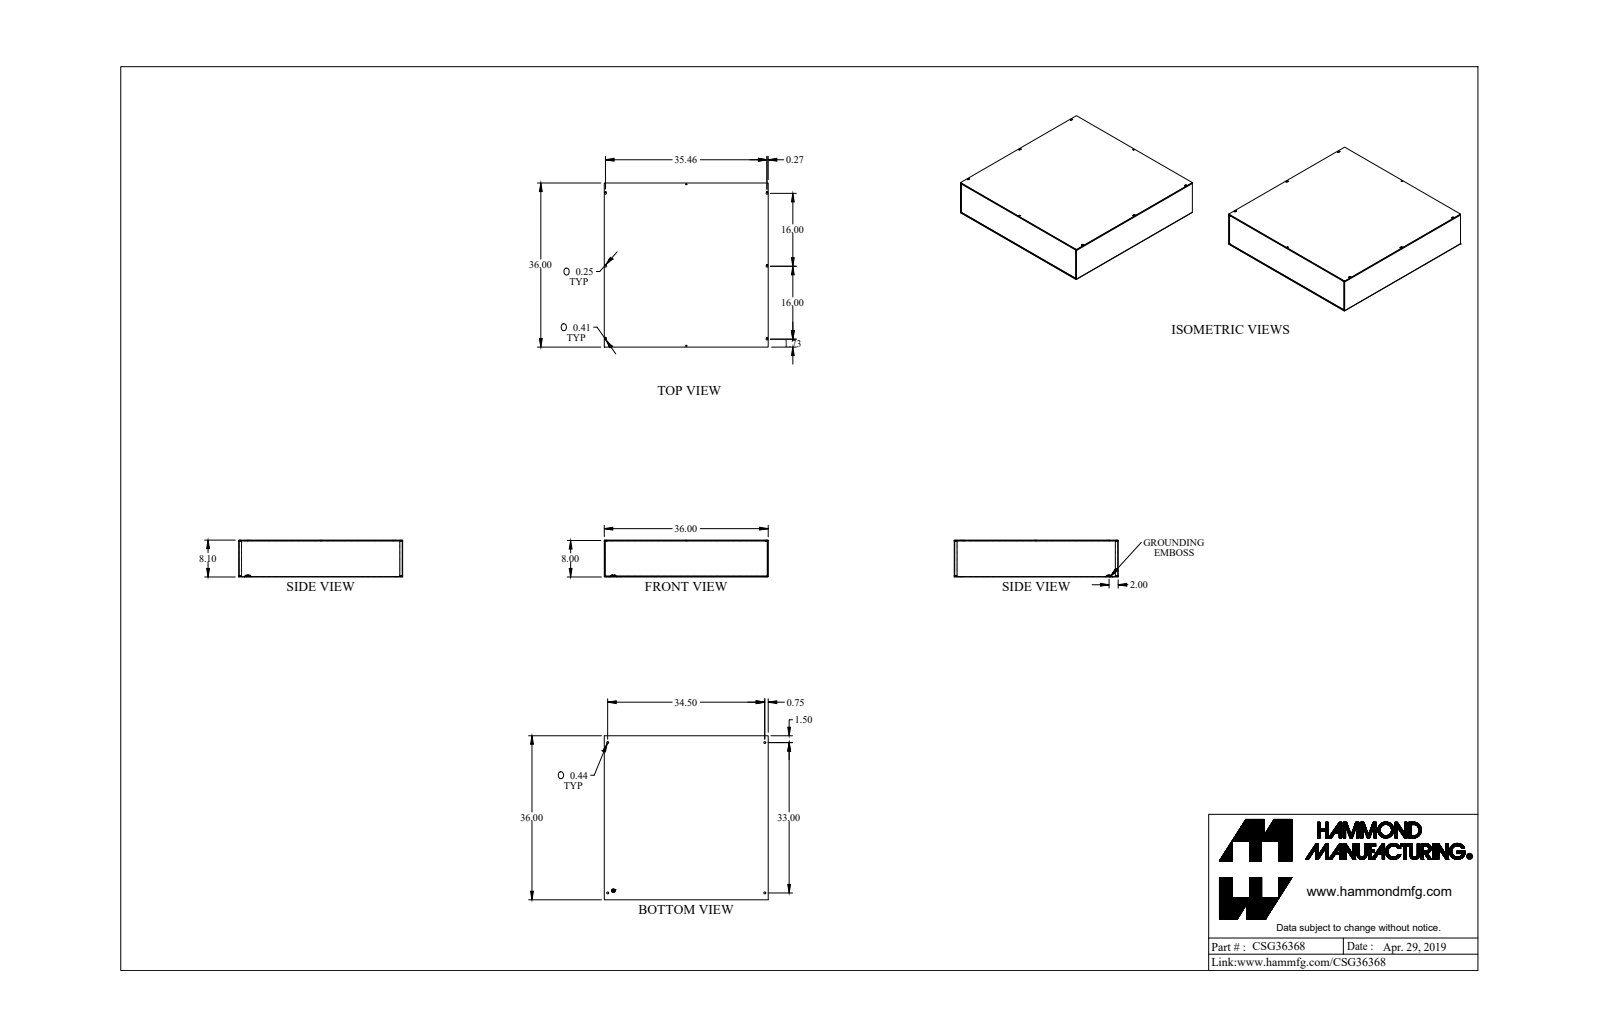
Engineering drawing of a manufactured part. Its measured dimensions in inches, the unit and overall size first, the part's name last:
Units: inches
Overall size (bounding box): 36 × 36 × 8.095
Round holes (diameter × count): ⌀0.17 ×9, ⌀0.437 ×4, ⌀0.25 ×2, ⌀0.5 ×1
Round bosses / shafts (diameter × count): ⌀0.492 ×1, ⌀0.36 ×1
Partial cylindrical surfaces — rounded edges, fillets, slot ends (radius × count): R0.048 ×12, R0.143 ×12, R0.095 ×8, R0.125 ×6, R0.203 ×6
Main face-to-face distances: 0.095, 8, 7.905, 8.095, 35.905, 36, 35.81, 0.19, 7.81, 0.11
Hole centre spacings: 0.693, 16, 16.507, 17.294, 17.814, 25.074, 32.504, 34.983
Volume: 363.1 in³ · Surface area: 7 695 in²
Bodies: 4 solids, 221 faces (121 planar, 92 cylindrical, 8 other)
Part name (STEP PRODUCT): CSG36368_Default
STEP written by: SolidWorks 2019 (CONFIG_CONTROL_DESIGN)
